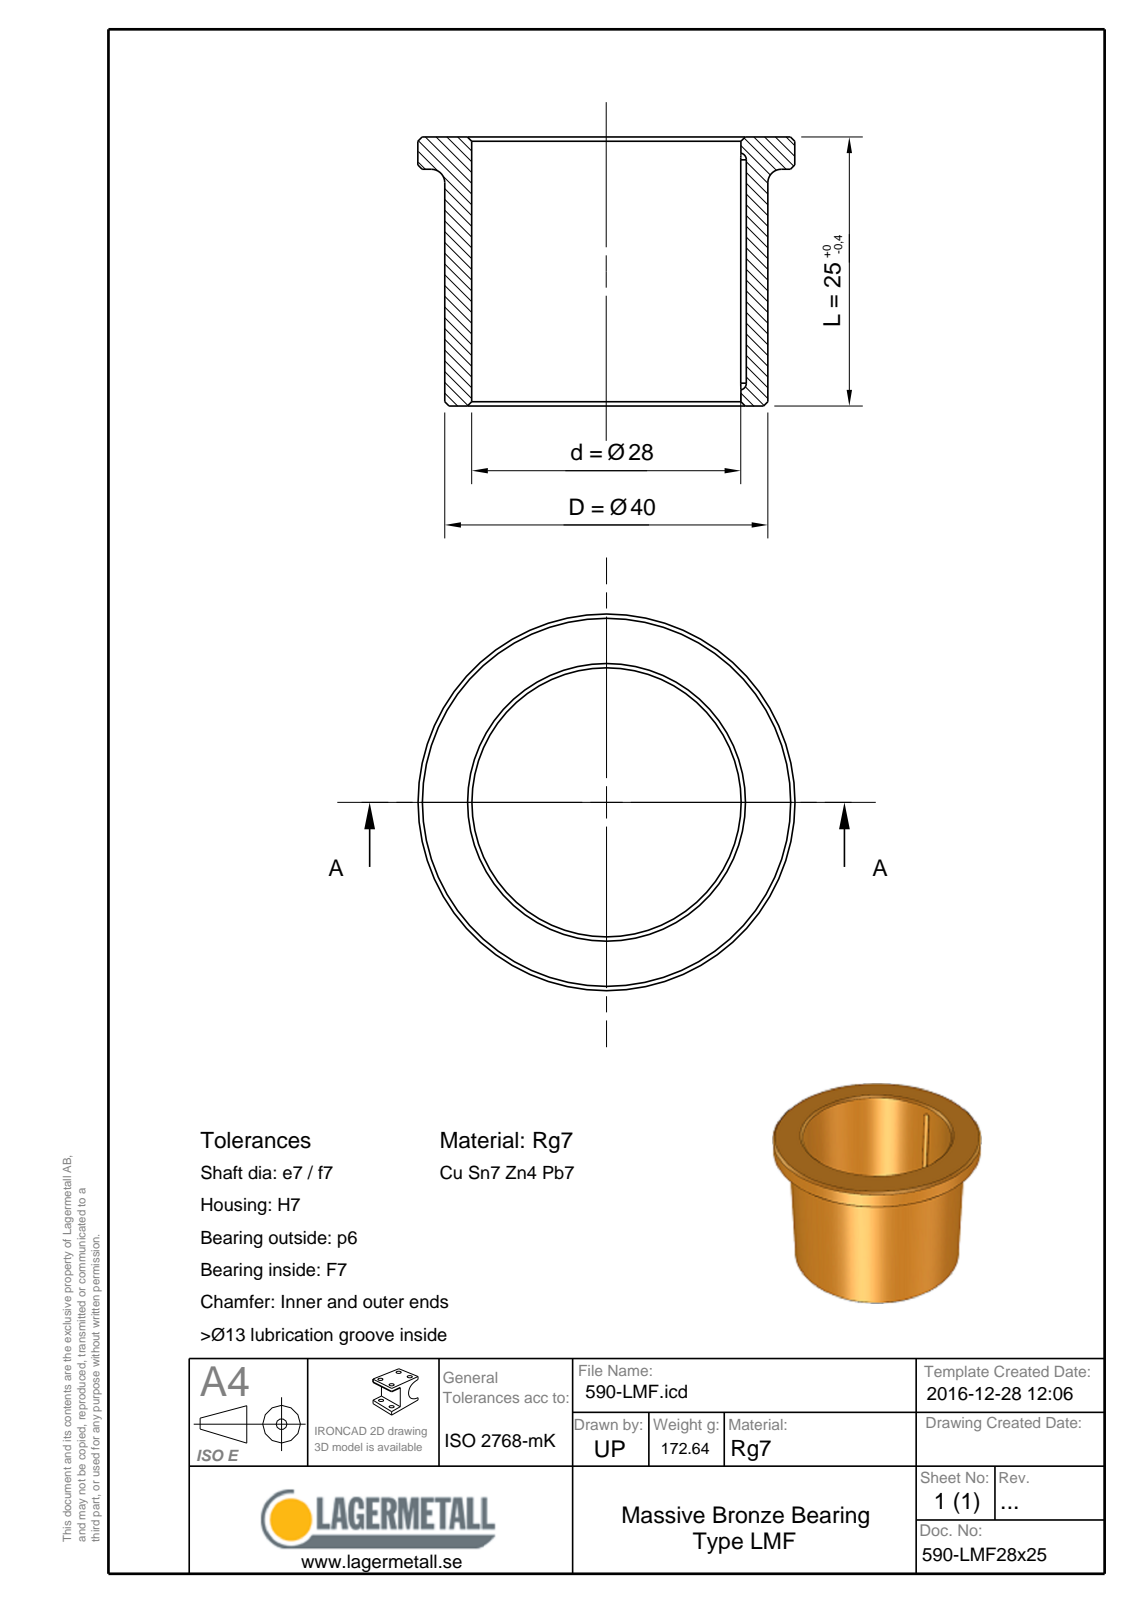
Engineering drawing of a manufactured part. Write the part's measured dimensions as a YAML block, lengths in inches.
part_name: "590-LMF28x25"
step_written_by: "Spatial InterOp 3D (CONFIG_CONTROL_DESIGN)"
units: inches
bodies: {solids: 1, faces: 17, planar: 4, cylindrical: 5, other: 8}
overall_size: [1.969, 1.969, 0.984]
volume: 1.197
surface_area: 12.25
round_holes:
  - {diameter: 1.102, count: 1}
round_bosses_or_shafts:
  - {diameter: 1.969, count: 1}
  - {diameter: 1.575, count: 1}
partial_cylinders:
  - {radius: 0.049, count: 2}
face_to_face_distances: [0.984, 0.787, 0.197]
